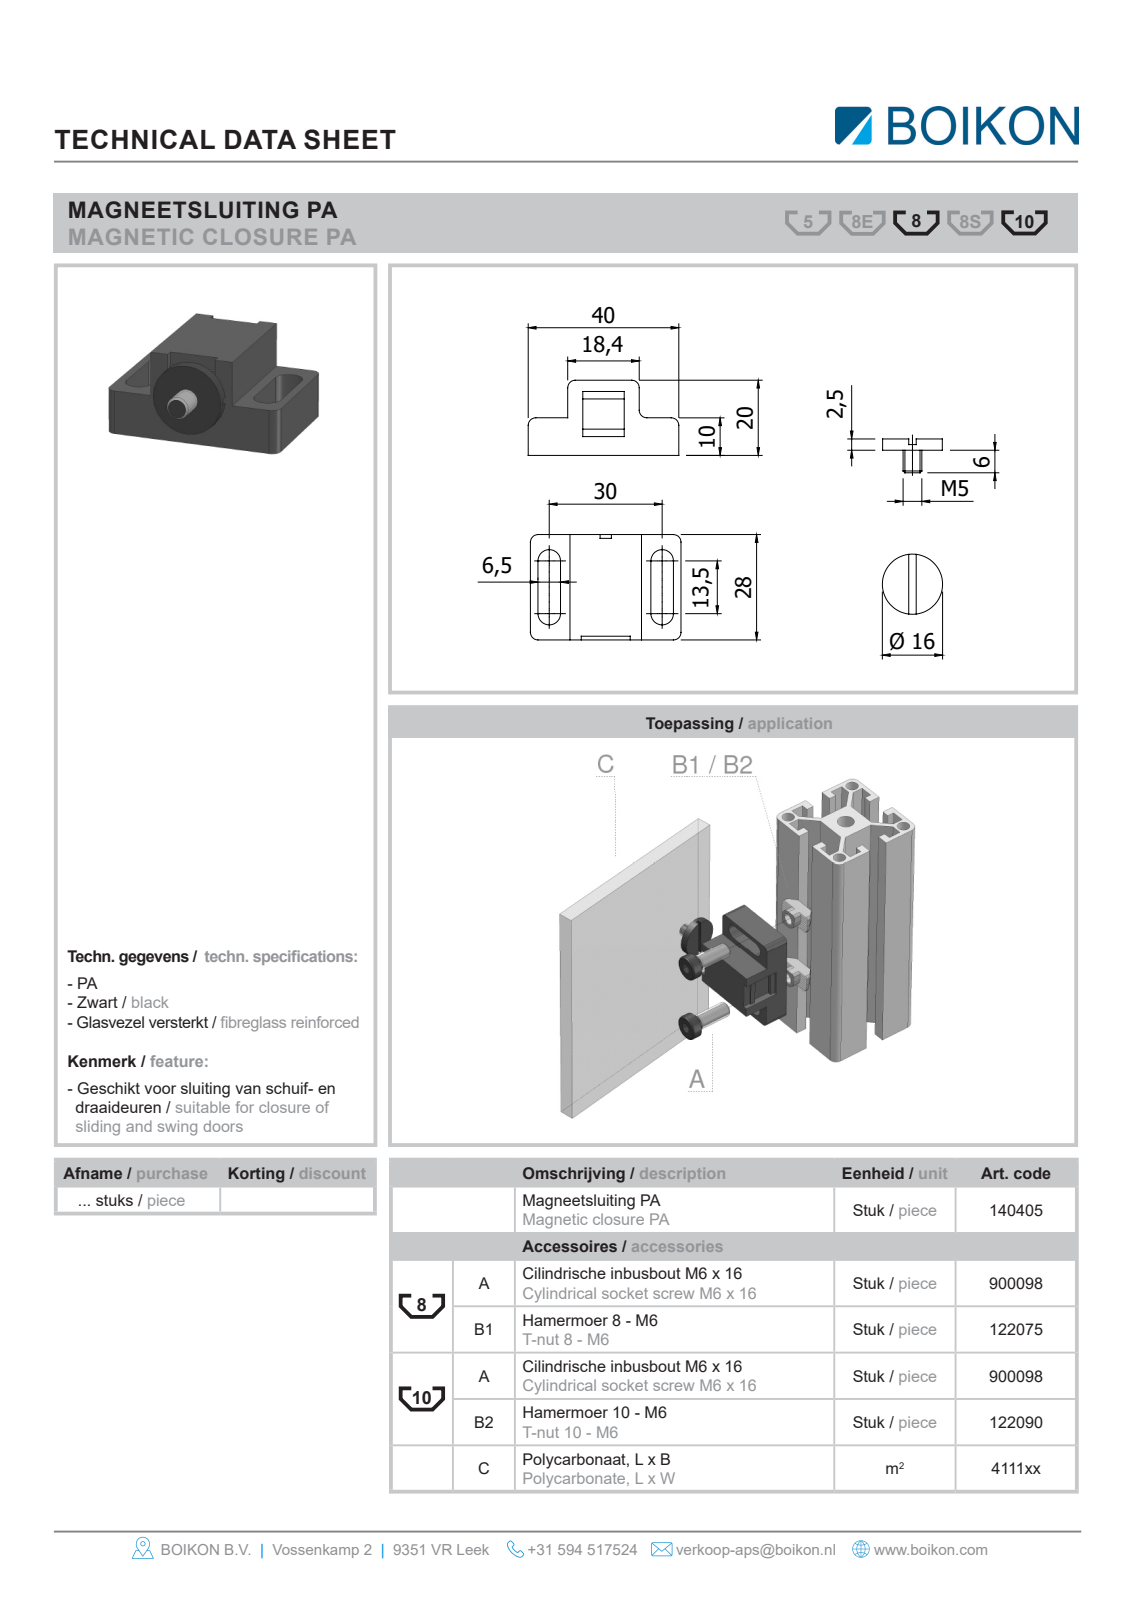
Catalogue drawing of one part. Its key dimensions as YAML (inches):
part_name: "Root; 140405Magneetsluiting PA zwartBOIKON"
step_written_by: "HiCAD 2013 1802.4 Build 509 (AUTOMOTIVE_DESIGN)"
units: inches
bodies: {solids: 2, faces: 57, planar: 46, cylindrical: 10, other: 1}
overall_size: [1.575, 1.449, 0.787]
volume: 0.749
surface_area: 9.622
round_bosses_or_shafts:
  - {diameter: 0.618, count: 1}
  - {diameter: 0.158, count: 1}
partial_cylinders:
  - {radius: 0.079, count: 4}
  - {radius: 0.122, count: 4}
face_to_face_distances: [0.394, 1.161, 0.787, 0.413, 1.102, 0.205, 0.583, 0.502, 1.004, 0.189]
